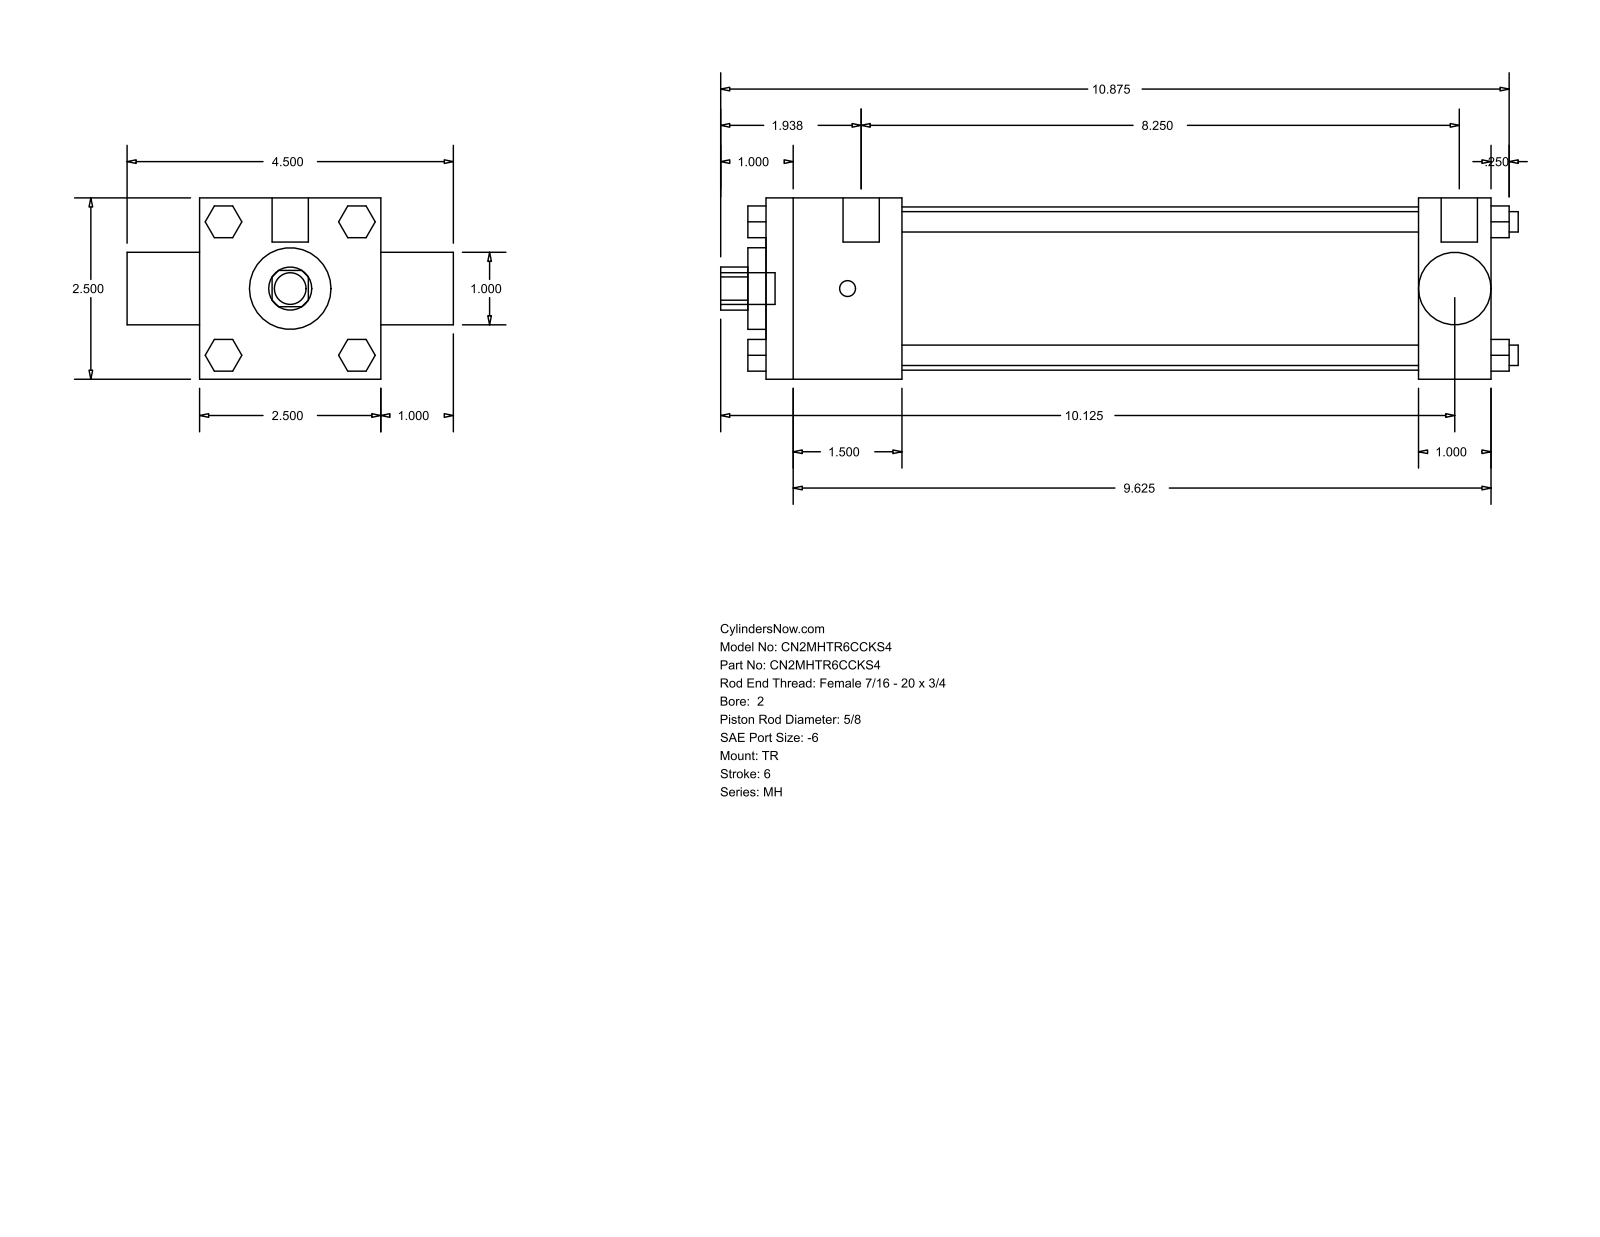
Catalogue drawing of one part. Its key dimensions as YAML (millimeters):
part_name: "MH_TR__0200_0.625"
step_written_by: "GSSL Pune (CONFIG_CONTROL_DESIGN)"
units: millimeters
bodies: {solids: 0, faces: 120, planar: 92, cylindrical: 28, other: 0}
overall_size: [279.4, 114.3, 63.5]
round_holes:
  - {diameter: 15.88, count: 1}
  - {diameter: 25.35, count: 1}
  - {diameter: 28.57, count: 1}
  - {diameter: 57.15, count: 1}
round_bosses_or_shafts:
  - {diameter: 7.14, count: 4}
  - {diameter: 5.56, count: 3}
  - {diameter: 12.7, count: 2}
  - {diameter: 11.11, count: 1}
partial_cylinders:
  - {radius: 7.54, count: 1}
face_to_face_distances: [63.5, 254, 47.62, 228.59, 180.97, 206.38, 25.41, 25.4, 260.35, 6.35]
